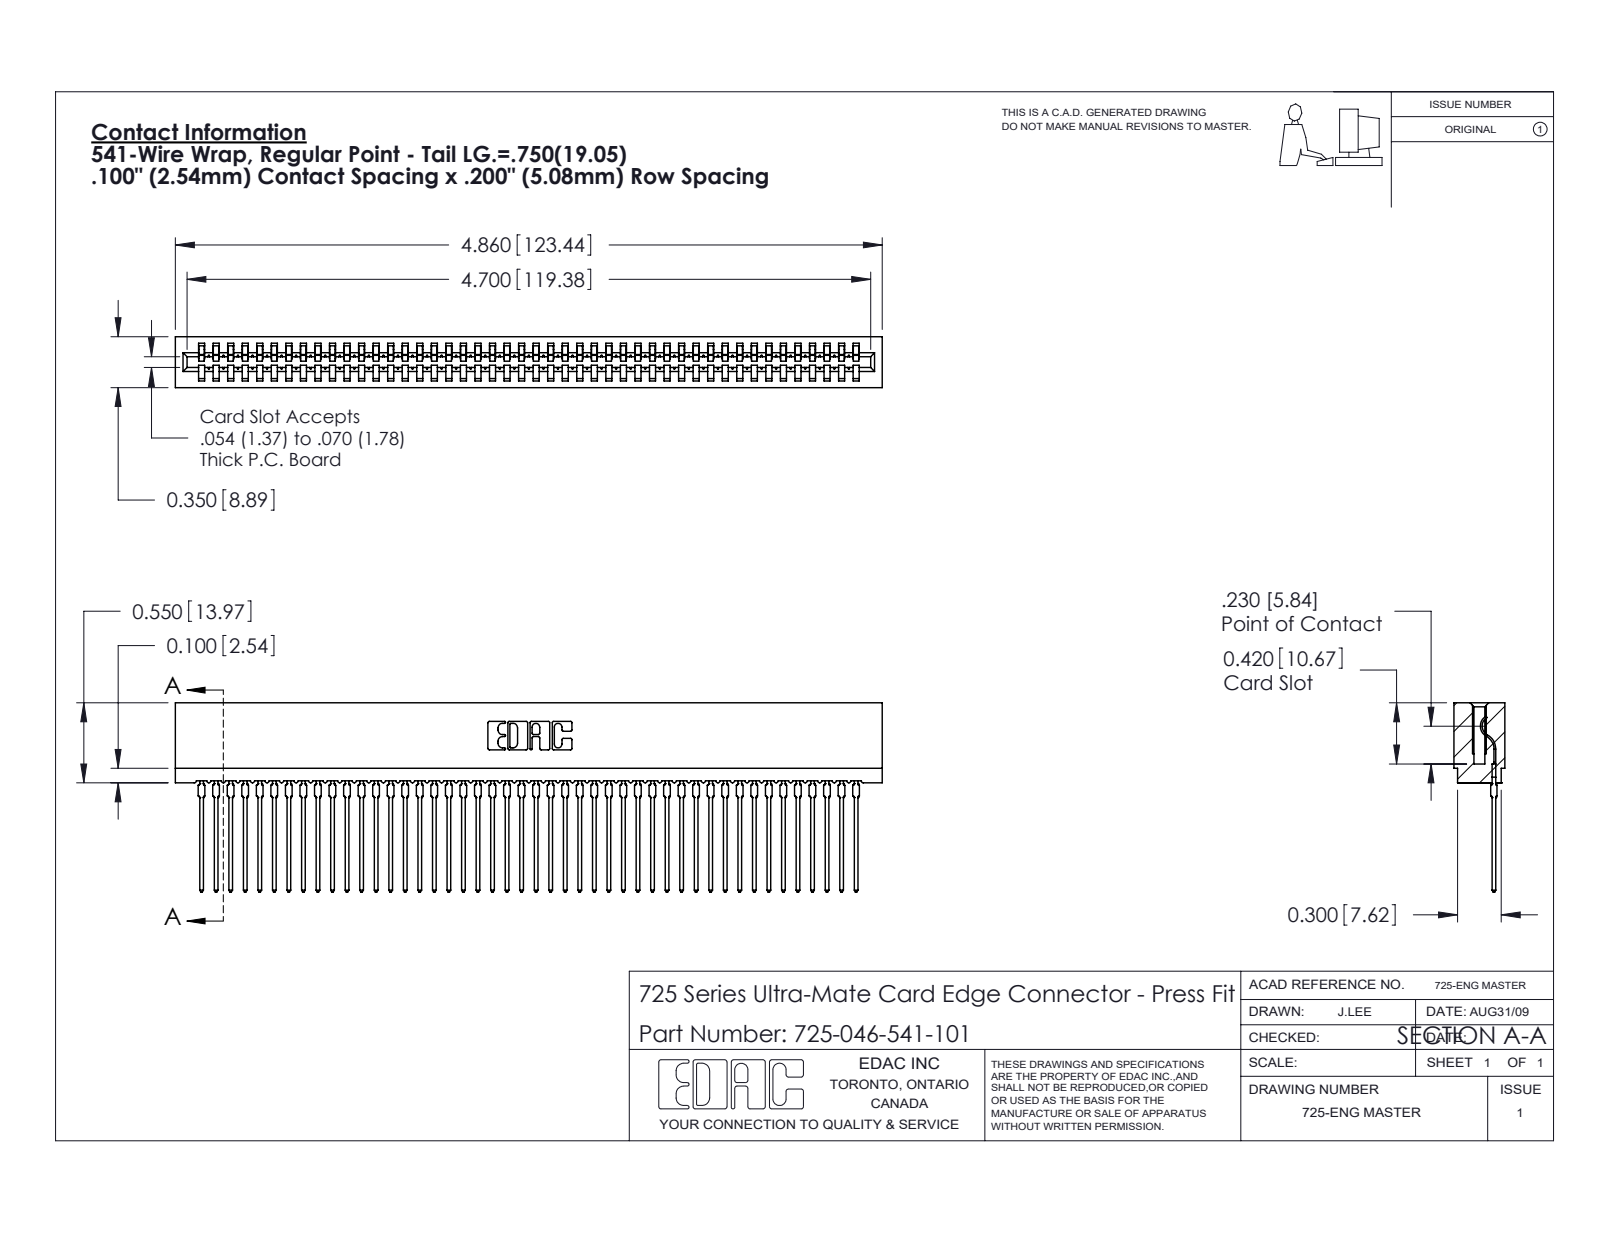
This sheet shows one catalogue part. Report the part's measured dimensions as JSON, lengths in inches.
{"part_name": "725 Part_Insulator Option - 01; 725-046-541-101; 745-292-001_541", "step_written_by": "SolidWorks 2020 (CONFIG_CONTROL_DESIGN)", "units": "inches", "bodies": {"solids": 47, "faces": 5247, "planar": 3137, "cylindrical": 914, "other": 1196}, "overall_size": [4.86, 1.301, 0.35], "volume_in3": 0.582, "surface_area_in2": 29.97, "partial_cylinders_radius": [[0.015, 92], [0.021, 92], [0.01, 22], [0.007, 6], [0.031, 6], [0.005, 4], [0.011, 4], [0.026, 3]], "face_to_face_distances": [0.35, 0.063, 0.287, 0.2, 0.212, 0.138, 0.1, 0.045, 0.305, 0.093]}
